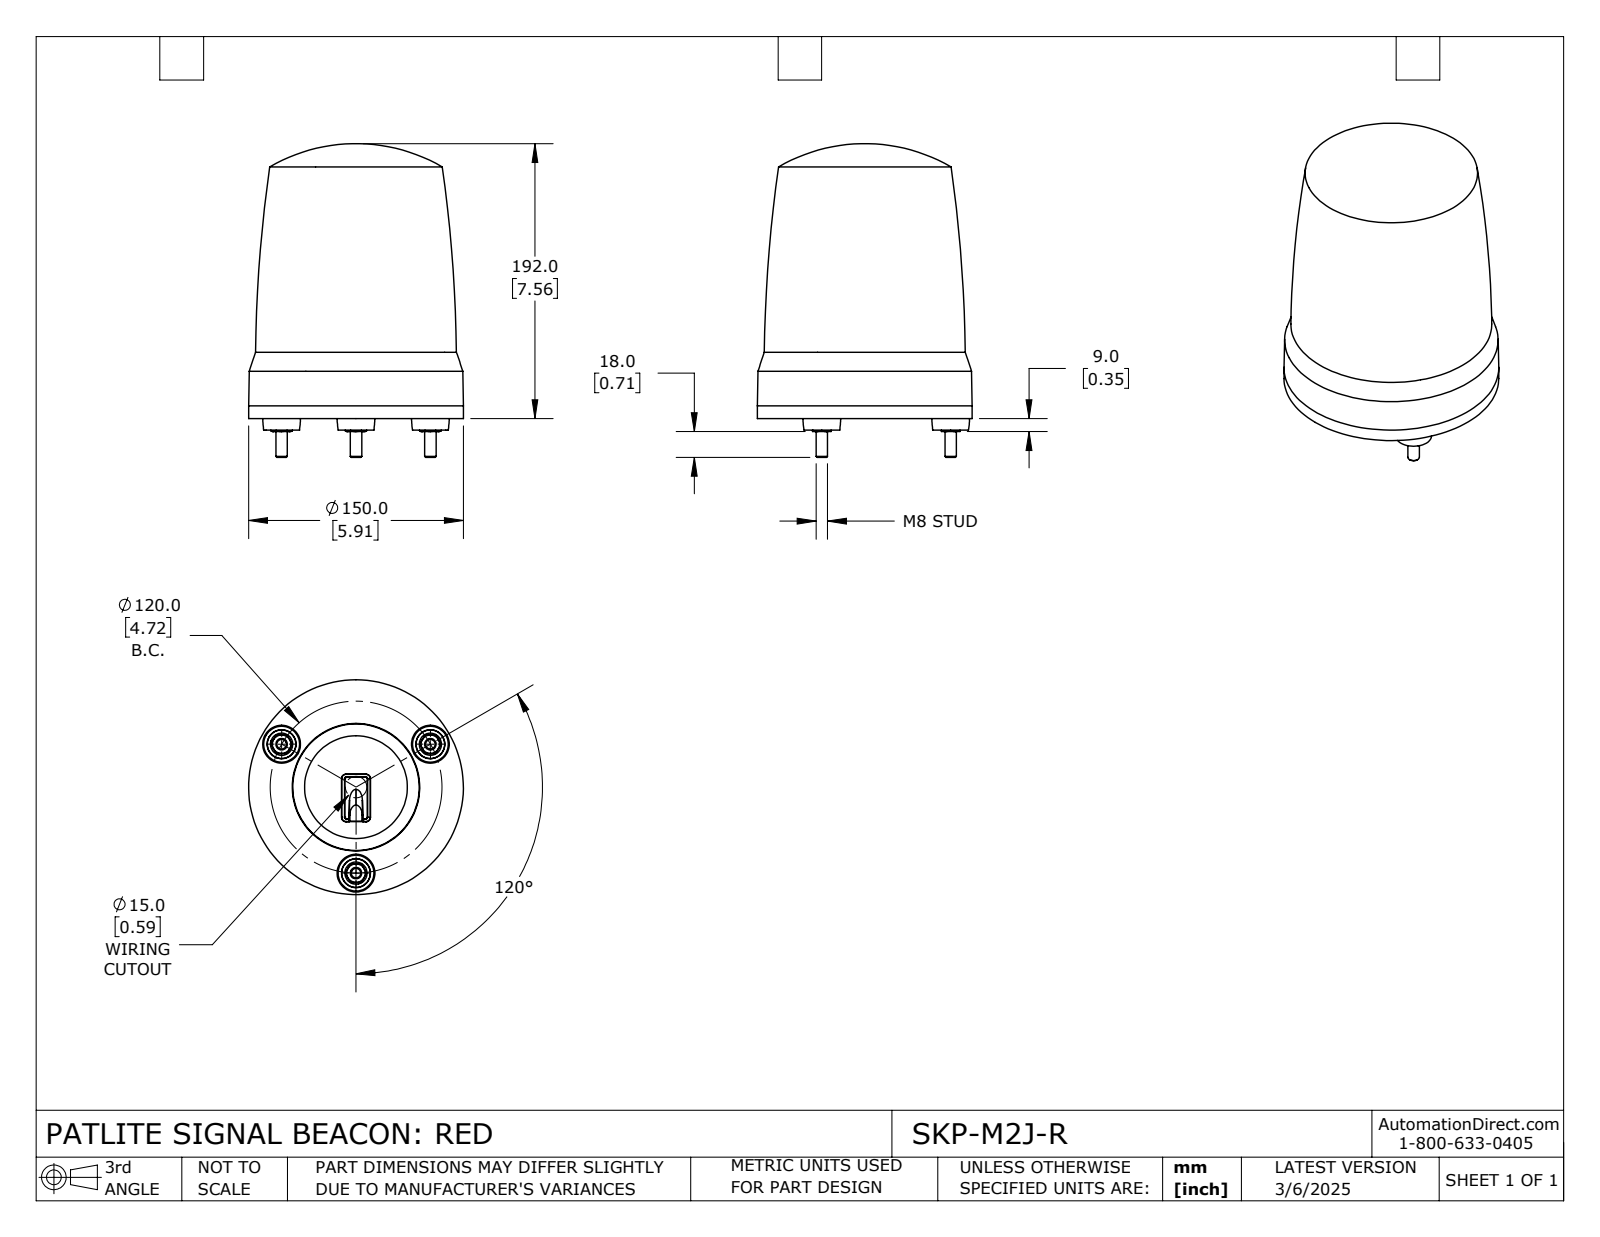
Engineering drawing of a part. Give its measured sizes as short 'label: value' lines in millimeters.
name: SKP-M2J-R
written by: SolidWorks 2024 (CONFIG_CONTROL_DESIGN)
unit: mm
bodies: 1 solid, 144 faces (49 planar, 14 cylindrical, 81 other)
size: 219 × 150 × 150
volume: 2 538 000 mm³; area: 119 026 mm²
bosses: 3× ⌀15.5, 3× ⌀8, 1× ⌀150
face distances: 32.7, 8, 40.7, 13, 7.1, 0.9, 33.6, 1.6, 36.05, 41.55
